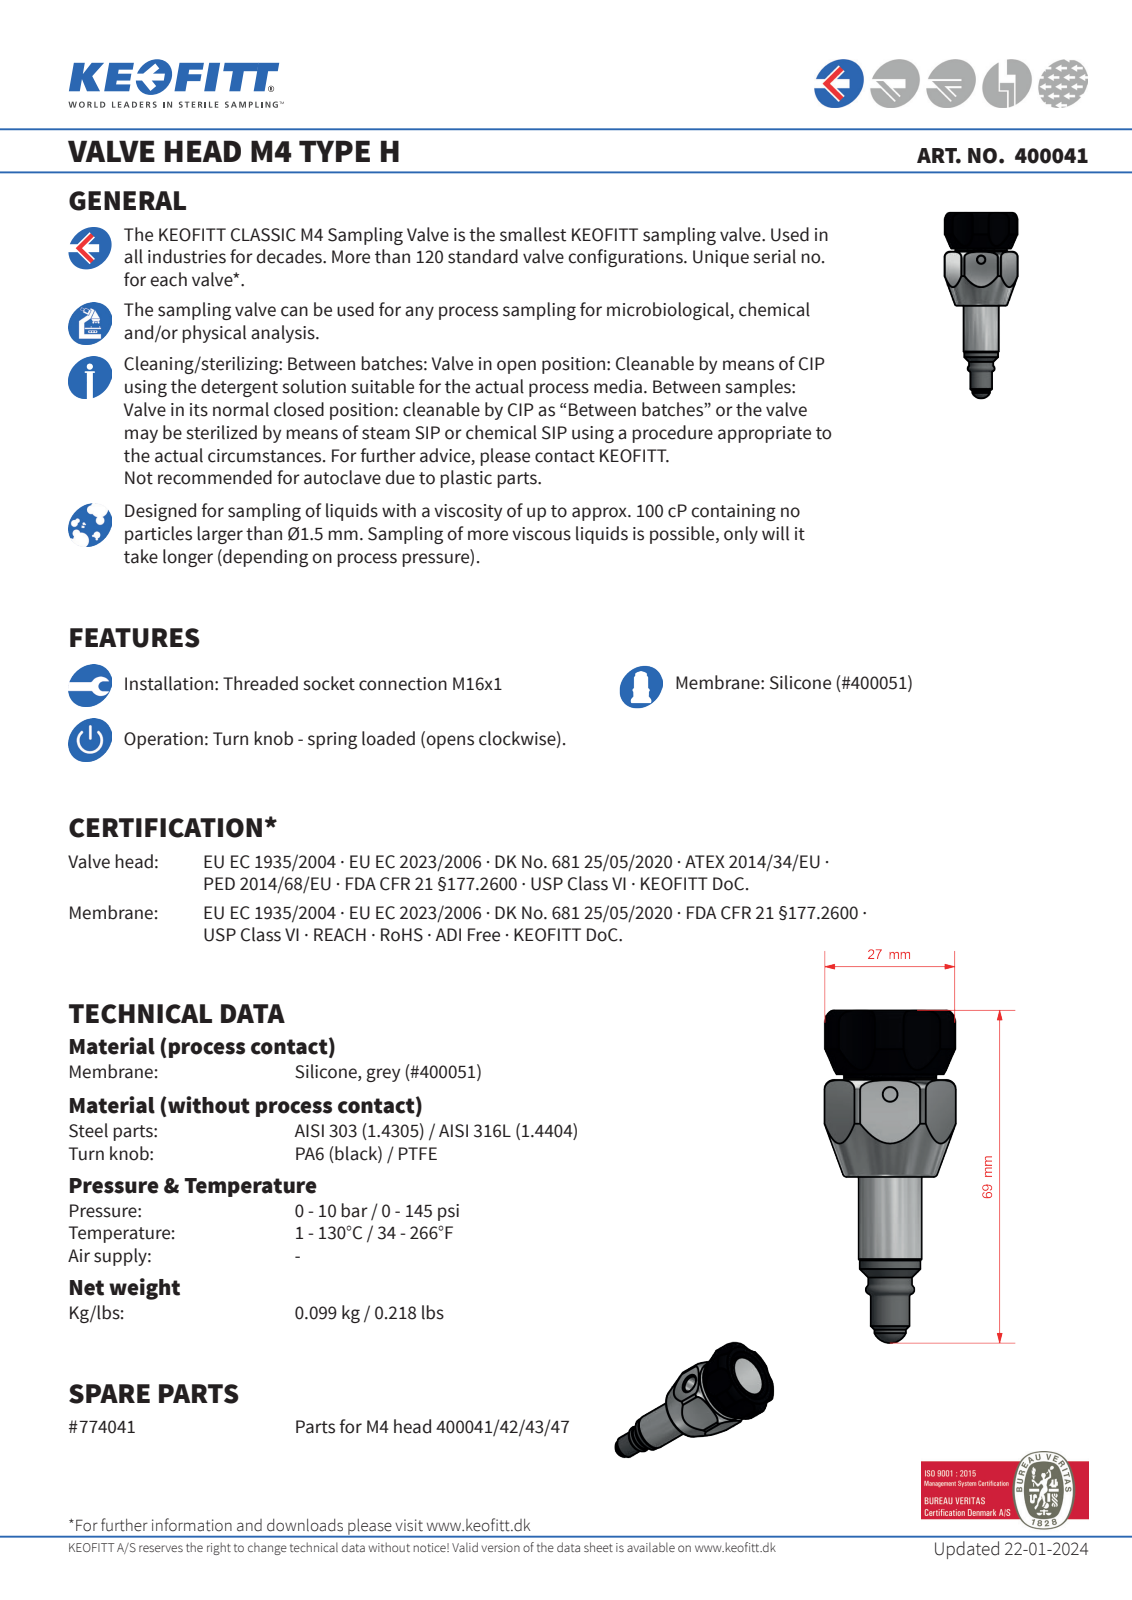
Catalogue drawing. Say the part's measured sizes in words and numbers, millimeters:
Its 3-D file was written by "Autodesk Inventor 2008 (AUTOMOTIVE_DESIGN)". It is 1 solid with 74 faces: 18 planar, 34 cylindrical and 22 other. Overall it measures 67.51 by 28 by 26.97 millimeters. Its volume is 18 480 cubic millimeters and its surface area 5 712 square millimeters. Round holes: 1 of diameter 3.05, 1 of diameter 6.1, 1 of diameter 14.92, 1 of diameter 15, 1 of diameter 16.5. Round bosses or shafts: 1 of diameter 19, 1 of diameter 16, 1 of diameter 13, 1 of diameter 12.5, 1 of diameter 12.03, 1 of diameter 9, 1 of diameter 8, 1 of diameter 6.5. Partial cylindrical surfaces (rounded edges, fillets, slot ends): 6 of radius 6, 1 of radius 8.84, 1 of radius 13.48, 1 of radius 14. The main face-to-face distances are 24, 12.69, 13.8, 1.11, 0.8, 14.31, 13.2, 0.51, 0.31, 13.49. The hole center spacings are 2.
